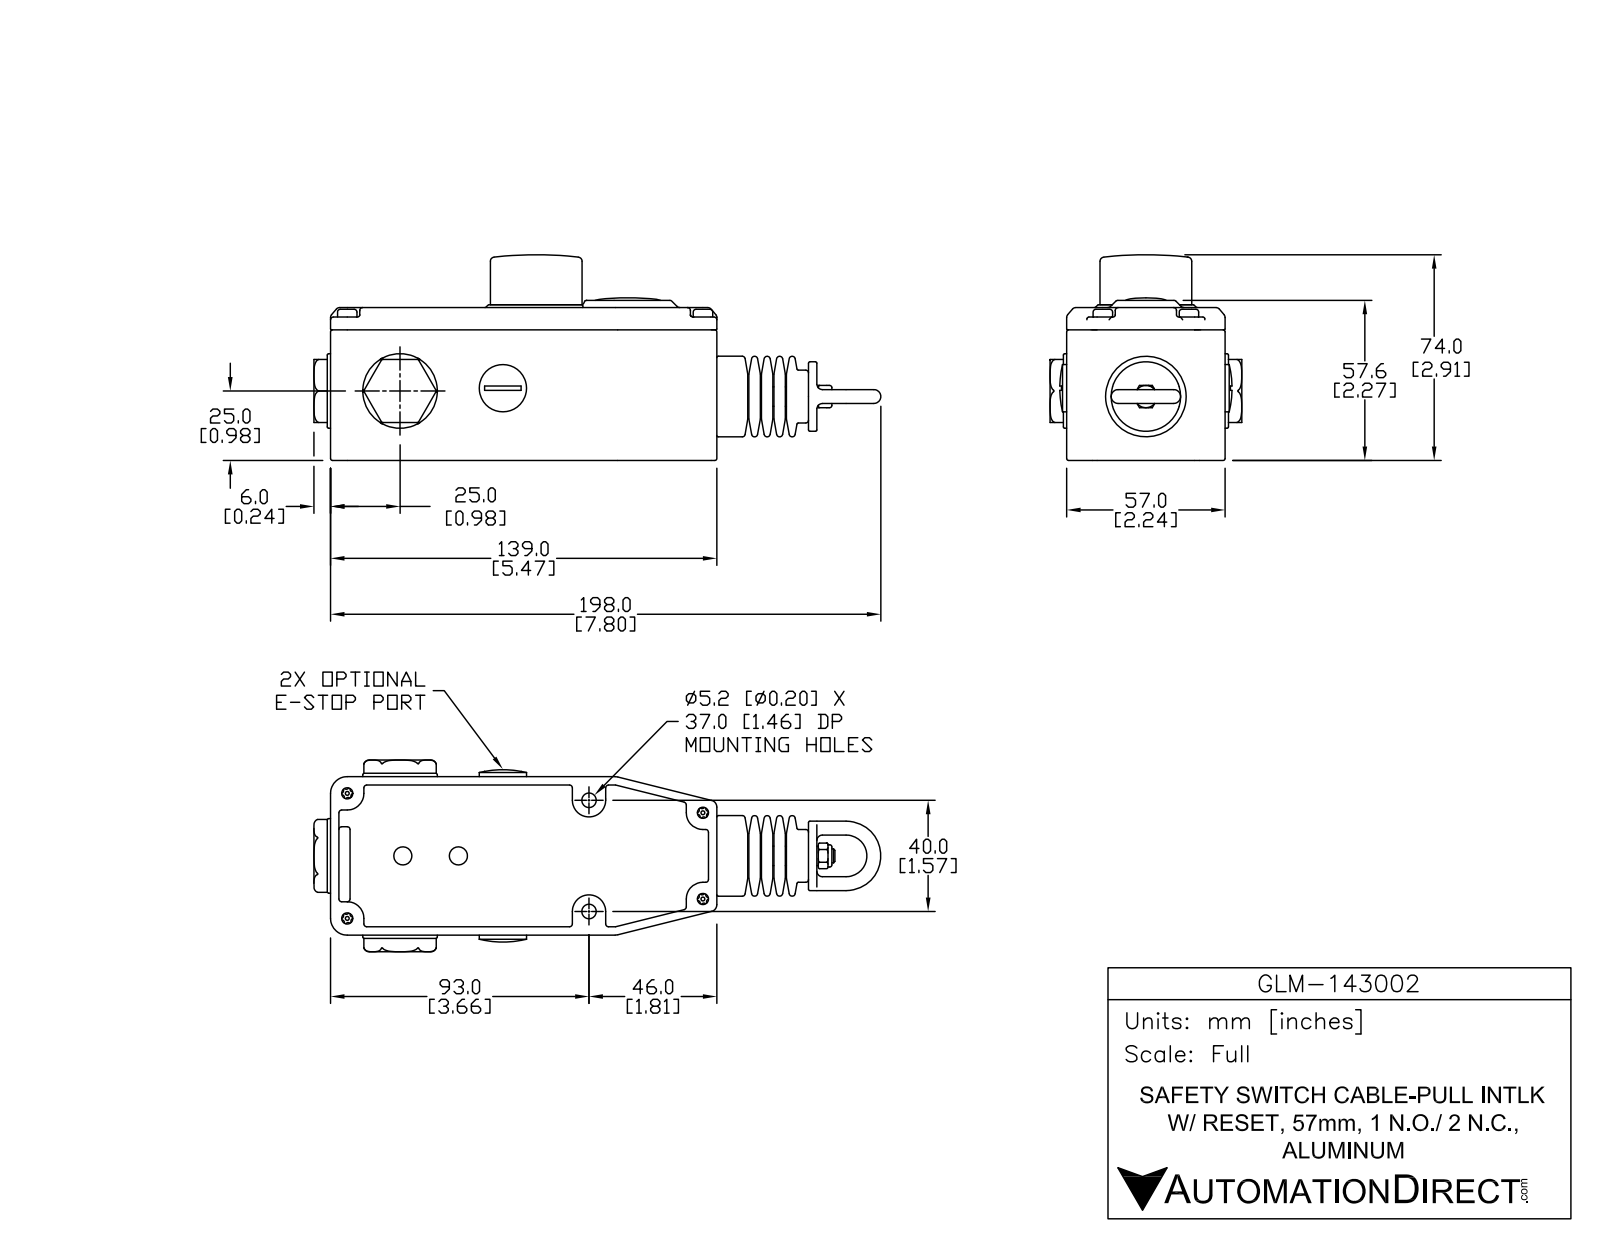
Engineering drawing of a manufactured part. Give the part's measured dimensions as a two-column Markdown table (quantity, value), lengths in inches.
| quantity | value |
| --- | --- |
| part name | GLM-143002 |
| STEP written by | SolidWorks 2013 (AUTOMOTIVE_DESIGN) |
| units | inches |
| bodies | 1 solid, 407 faces (126 planar, 146 cylindrical, 135 other) |
| overall size | 7.609 × 2.953 × 2.74 |
| volume | 27.43 in³ |
| surface area | 72.43 in² |
| round holes (diameter × count) | 0.157 × 4, 0.205 × 2 |
| round bosses / shafts (diameter × count) | 0.276 × 5, 1.055 × 2, 0.197 × 2, 1.386 × 1, 1.299 × 1, 1.142 × 1, 0.984 × 1, 0.748 × 1 |
| partial cylindrical surfaces (radius × count) | 0.02 × 30, 0.006 × 19, 0.01 × 12, 0.039 × 8, 0.177 × 2, 0.18 × 2, 0.276 × 2, 0.512 × 2 |
| main face-to-face distances | 2.153, 2.244, 2.165, 0.013, 5.472, 0.248, 2.492, 5.709, 0.236, 0.118 |
| hole center spacings | 1.624, 2.135, 3.427, 3.812, 5.047, 5.257, 1.22, 1.575 |
